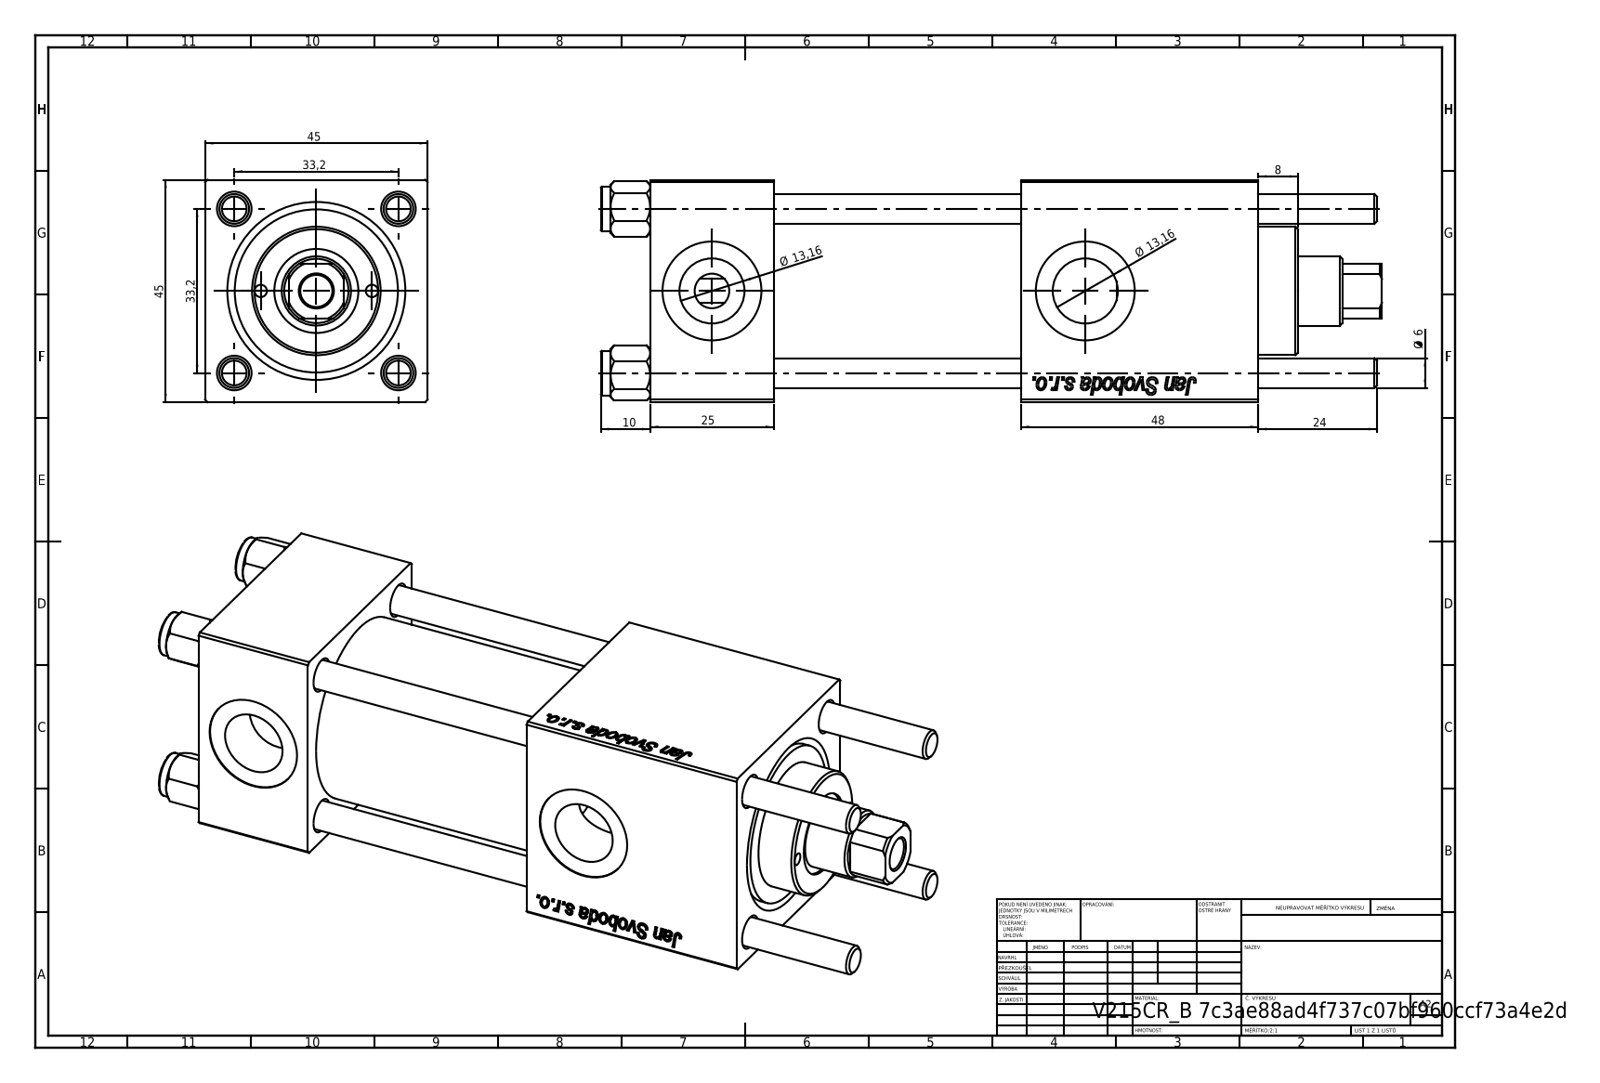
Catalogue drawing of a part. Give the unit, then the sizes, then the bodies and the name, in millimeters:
Units: millimetres
Overall size (bounding box): 158 × 45 × 45
Round holes (diameter × count): ⌀6 ×4, ⌀2.5 ×2, ⌀7 ×2, ⌀13.16 ×2, ⌀20 ×2, ⌀6.5 ×1, ⌀14 ×1, ⌀17 ×1, ⌀24 ×1, ⌀32 ×1, ⌀33 ×1
Round bosses / shafts (diameter × count): ⌀9 ×4, ⌀38 ×1, ⌀26 ×1
Partial cylindrical surfaces — rounded edges, fillets, slot ends (radius × count): R6.5 ×1
Main face-to-face distances: 45, 25, 123, 98, 50, 75, 48, 94.3, 69.3, 19.3
Hole centre spacings: 17.44, 23.48, 32.42, 33.2, 11.25, 46.95, 22.5, 75.5
Volume: 198 244 mm³ · Surface area: 72 776 mm²
Bodies: 11 solids, 1163 faces (433 planar, 82 cylindrical, 648 other)
Part name (STEP PRODUCT): V215CR_B-1; V215_VC_A; V215CR_VCP_B; V215CR_B_TYCINKA (+1 more)
STEP written by: SolidWorks 2019 (CONFIG_CONTROL_DESIGN)
